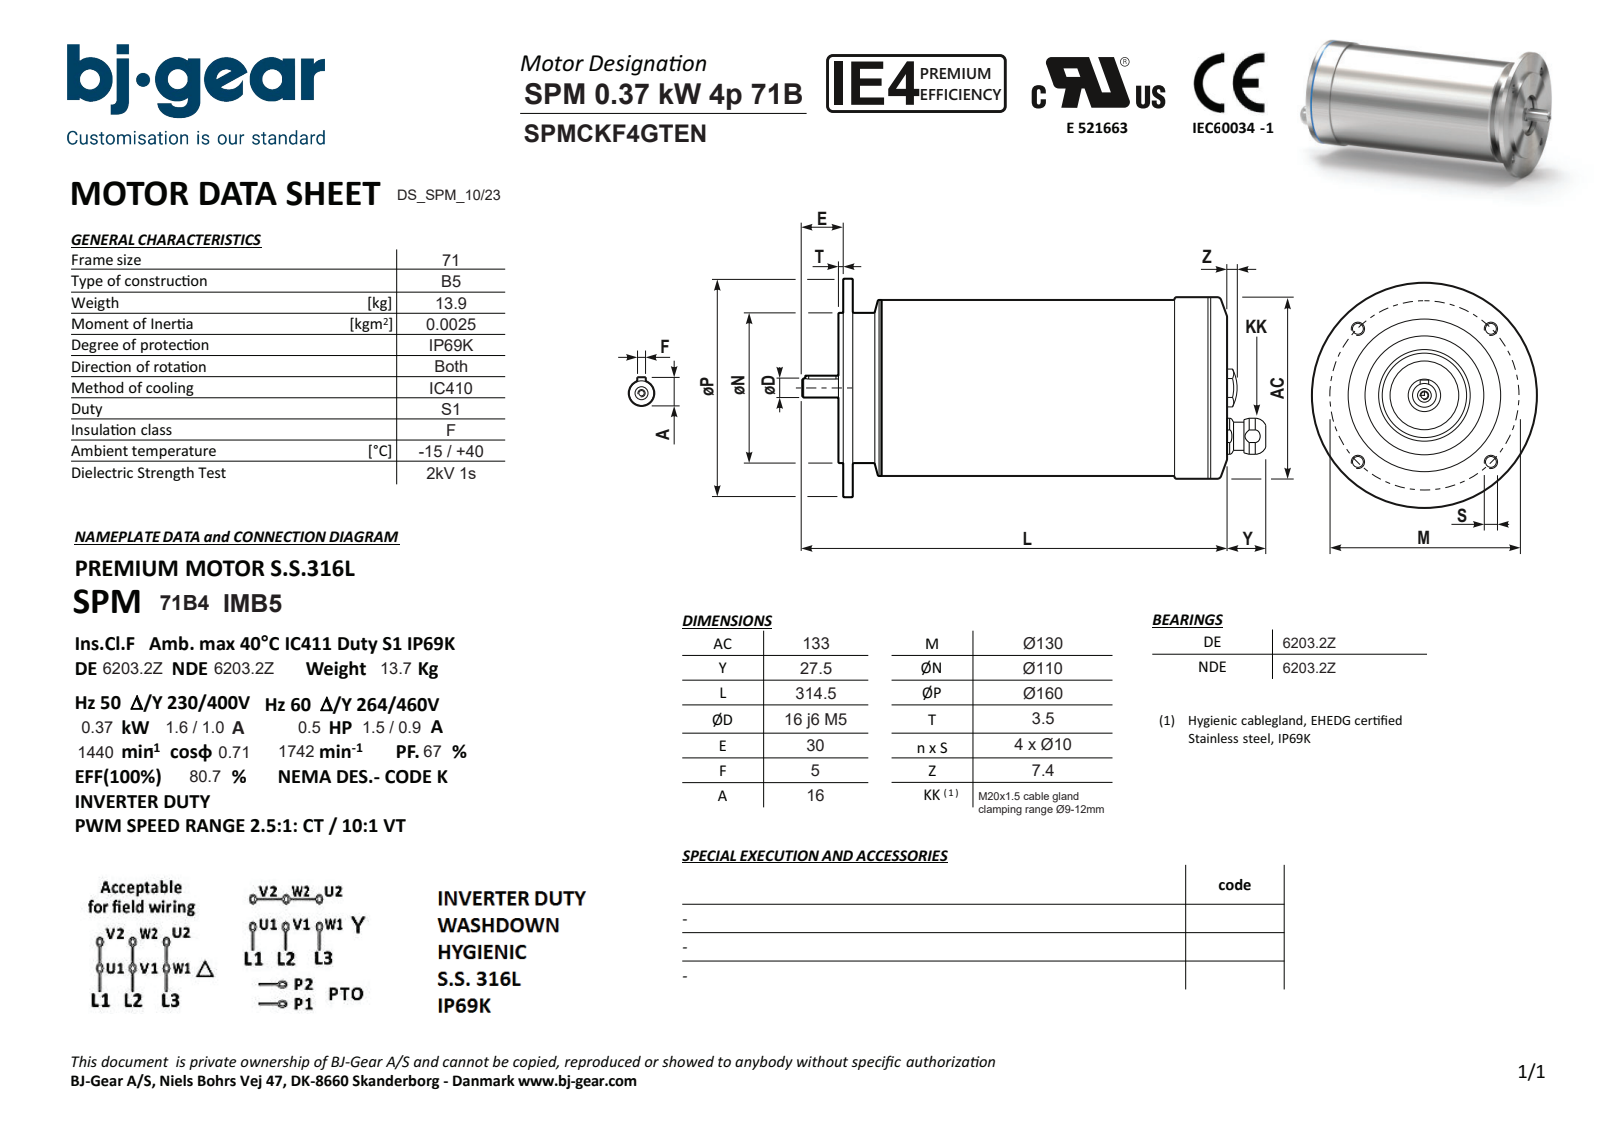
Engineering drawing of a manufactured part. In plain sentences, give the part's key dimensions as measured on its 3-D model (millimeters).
The part is named "SPMCKF4GTENN4KSA1-N---NNN". Its 3-D file was written by "Solid Edge (AUTOMOTIVE_DESIGN)". It is 1 solid with 86 faces: 31 planar, 30 cylindrical and 25 other. Overall it measures 342 by 160 by 160 millimeters. Its volume is 3 756 000 cubic millimeters and its surface area 167 604 square millimeters. Round holes: 4 of diameter 10, 1 of diameter 4.13, 1 of diameter 5.3, 1 of diameter 7, 1 of diameter 13.4, 1 of diameter 52. Round bosses or shafts: 1 of diameter 160, 1 of diameter 133, 1 of diameter 132.98, 1 of diameter 129, 1 of diameter 128.98, 1 of diameter 110, 1 of diameter 20, 1 of diameter 17. Partial cylindrical surfaces (rounded edges, fillets, slot ends): 2 of radius 2.5, 1 of radius 12.8. The main face-to-face distances are 7, 277.5, 284.5, 288, 10.5, 3.5, 279, 1.5, 5.5, 9. The hole center spacings are 65, 91.92, 47.49, 92.23, 129.99, 34.
